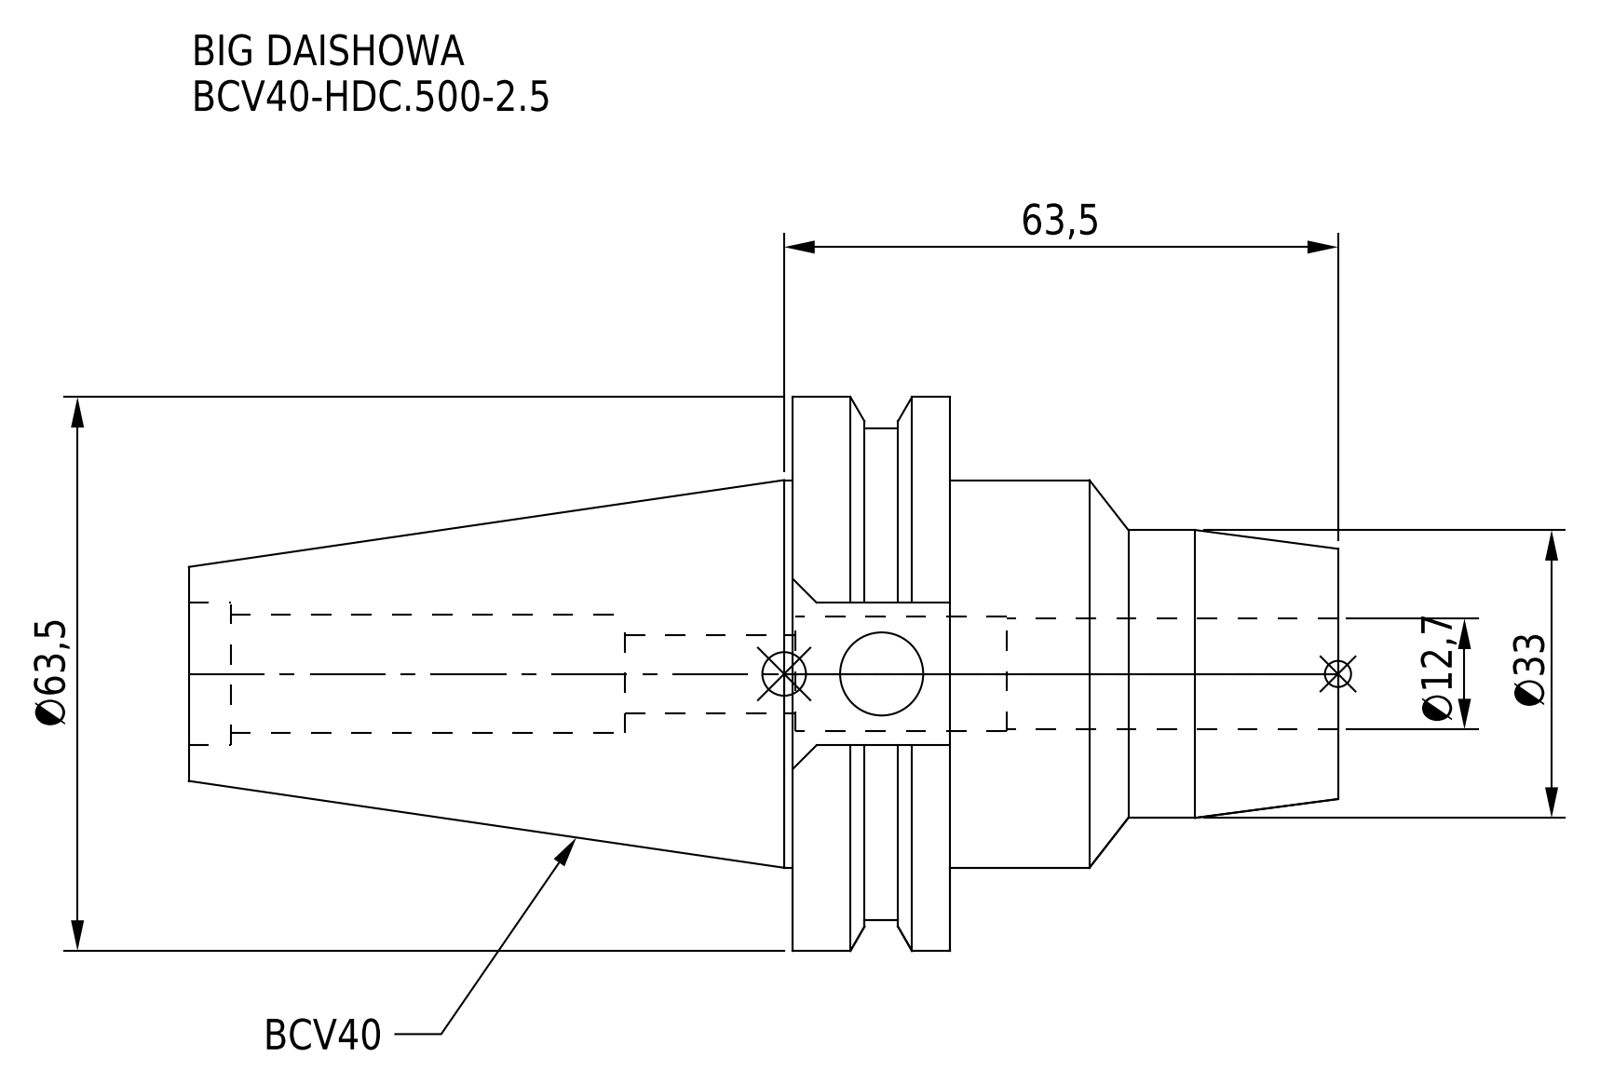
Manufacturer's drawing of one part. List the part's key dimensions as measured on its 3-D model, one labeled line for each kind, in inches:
Part name (STEP PRODUCT): BCV40-HDC_500-2_5
STEP written by: CREO PARAMETRIC BY PTC INC, 2016380 (AUTOMOTIVE_DESIGN)
Units: inches
Bodies: 1 solid, 59 faces (23 planar, 26 cylindrical, 10 other)
Overall size (bounding box): 5.187 × 2.5 × 2.415
Volume: 9.075 in³ · Surface area: 41.41 in²
Round holes (diameter × count): ⌀0.354 ×1, ⌀0.375 ×1, ⌀0.5 ×1, ⌀0.52 ×1, ⌀0.535 ×1, ⌀0.643 ×1
Round bosses / shafts (diameter × count): ⌀2.5 ×1, ⌀2.219 ×1, ⌀1.75 ×1, ⌀1.299 ×1
Main face-to-face distances: 0.711, 1.75, 2.461, 5.187, 3.437, 2.726, 1.872, 0.645, 2.137, 0.387
